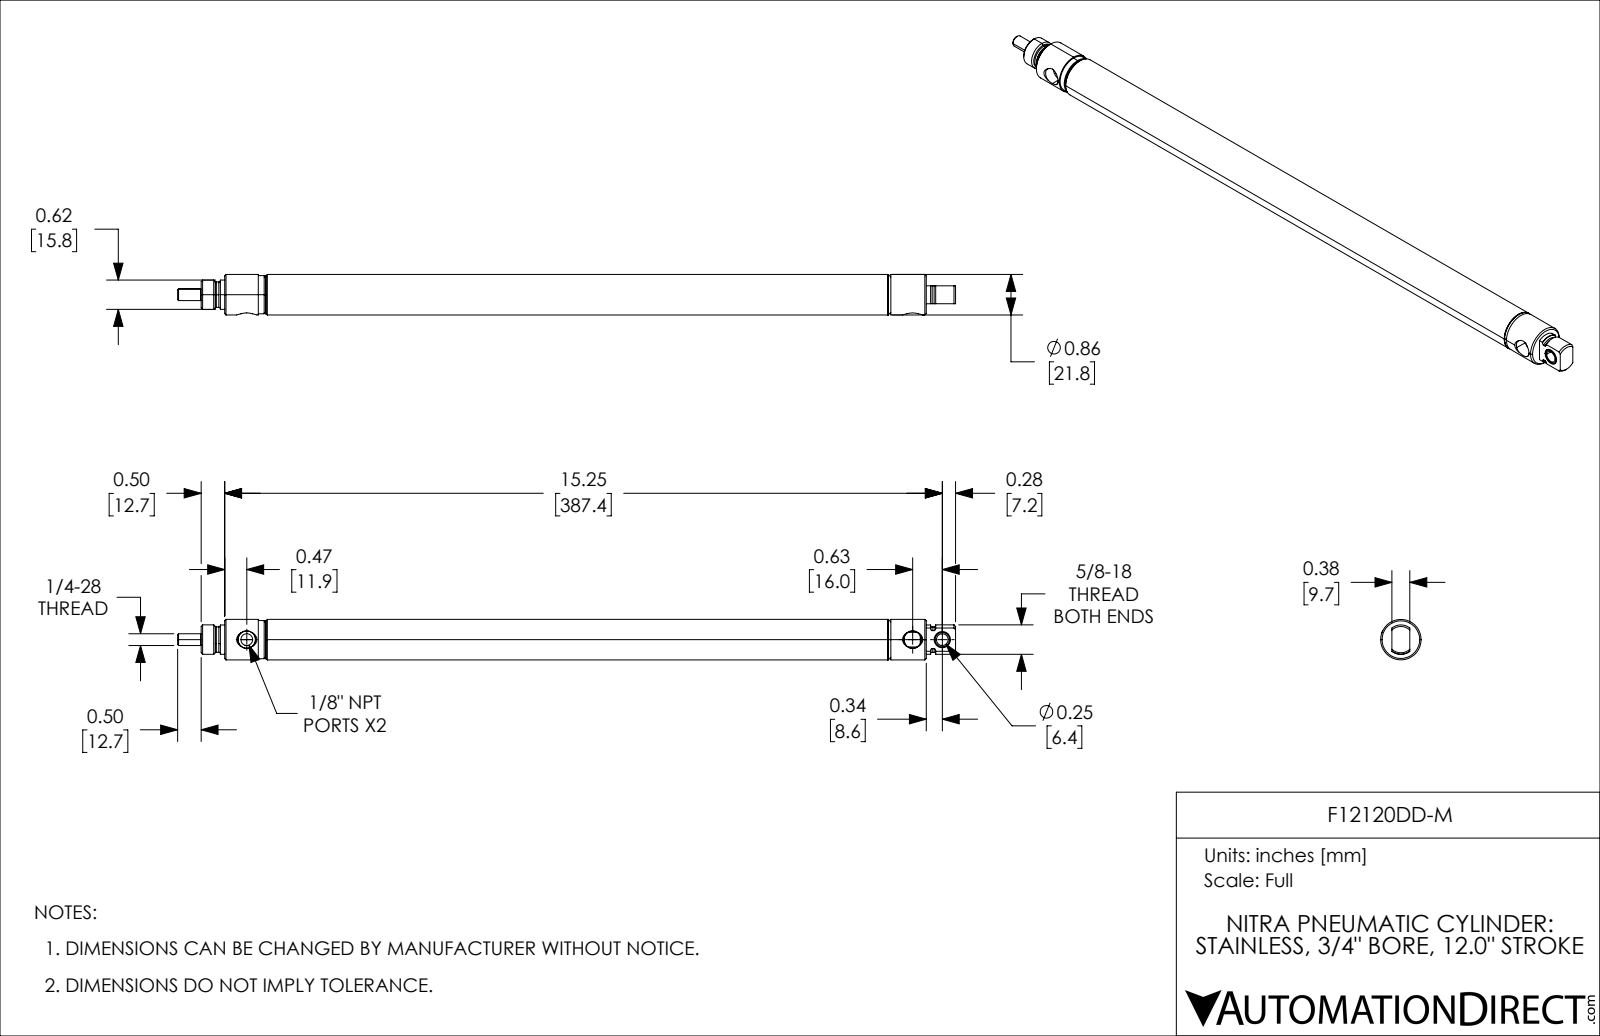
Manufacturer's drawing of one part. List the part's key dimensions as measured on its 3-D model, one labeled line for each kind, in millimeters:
Part name (STEP PRODUCT): F12120DD-M_9; F12120DD-M_7; F12120DD-M_11; F12120DD-M_3 (+2 more)
STEP written by: SolidWorks 2021 (CONFIG_CONTROL_DESIGN)
Units: millimetres
Bodies: 5 solids, 158 faces (29 planar, 61 cylindrical, 68 other)
Overall size (bounding box): 419.91 × 21.84 × 21.84
Volume: 63 488 mm³ · Surface area: 61 967 mm²
Round holes (diameter × count): ⌀6.35 ×1, ⌀6.38 ×1, ⌀6.95 ×1, ⌀7.92 ×1, ⌀8.78 ×1, ⌀9.23 ×1, ⌀12.7 ×1, ⌀17.83 ×1
Round bosses / shafts (diameter × count): ⌀21.84 ×1, ⌀20.57 ×1, ⌀19.35 ×1, ⌀15.88 ×1, ⌀15.81 ×1, ⌀13.68 ×1, ⌀6.35 ×1, ⌀5.84 ×1
Partial cylindrical surfaces — rounded edges, fillets, slot ends (radius × count): R6.84 ×1
Main face-to-face distances: 21.43, 40.49, 366.72, 304.8, 326.23, 350.92, 46.12, 24.69, 12.7, 9.66
Hole centre spacings: 16, 359.41, 375.41
